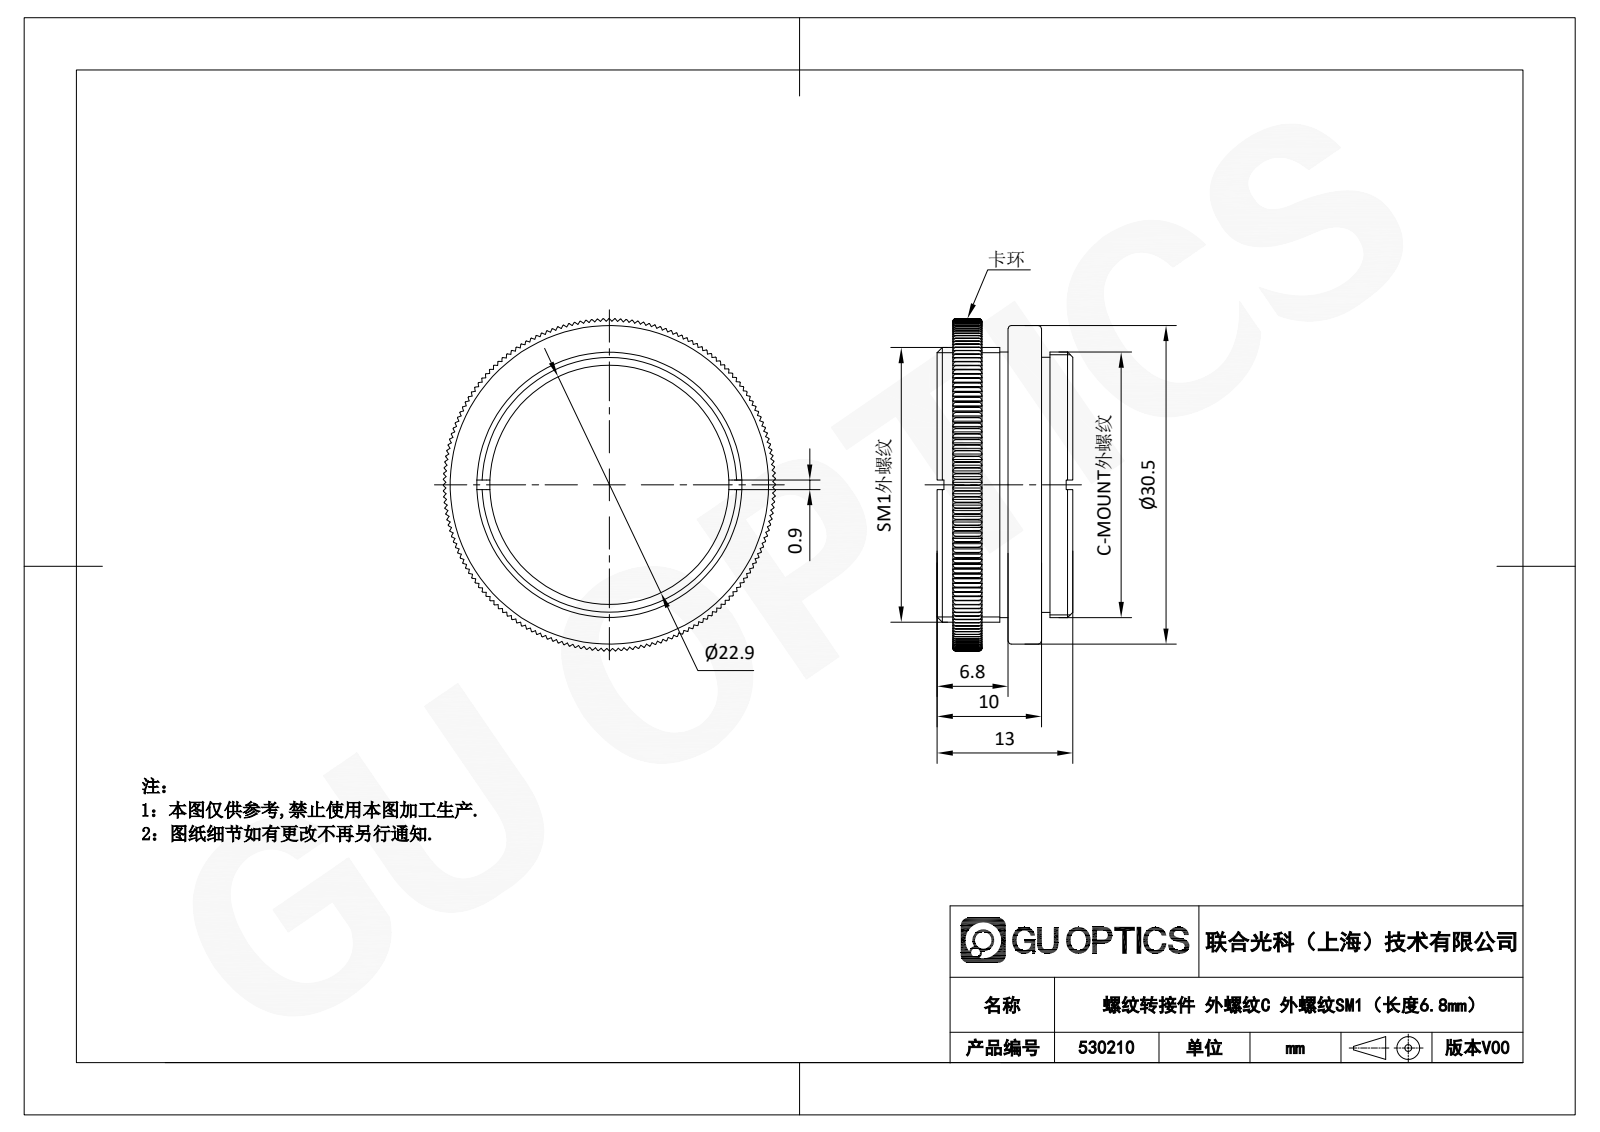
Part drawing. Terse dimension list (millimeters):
name: 530210; SM1NR
written by: SolidWorks 2020 (CONFIG_CONTROL_DESIGN)
unit: mm
bodies: 2 solids, 583 faces (382 planar, 187 cylindrical, 14 other)
size: 31.8 × 31.8 × 13
volume: 2 762 mm³; area: 3 775 mm²
holes: 1× ⌀22.9, 1× ⌀26.29
bosses: 1× ⌀30.5, 1× ⌀25.4, 1× ⌀24.4
rounds: 1× R15.9
face distances: 3.2, 5.3, 8.5, 2.8, 2.5, 5.7, 22.13, 22.14, 0.8, 4
